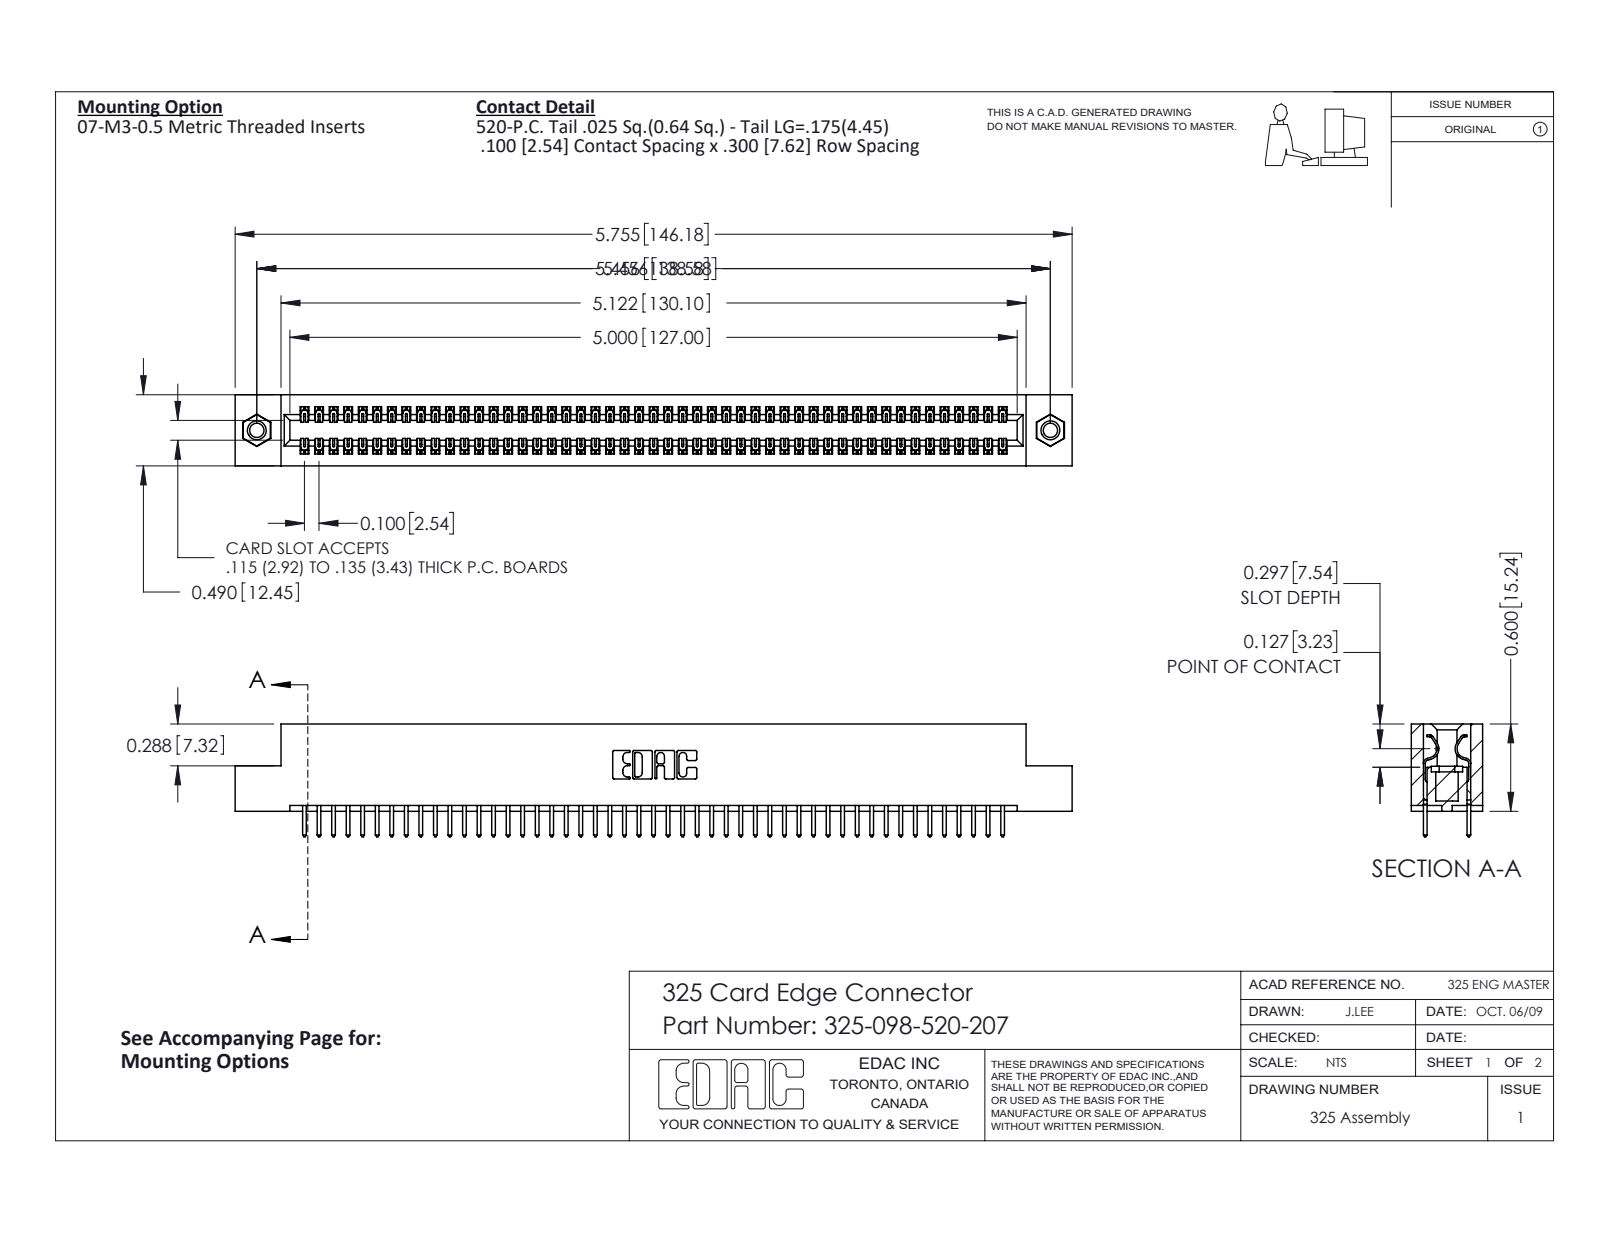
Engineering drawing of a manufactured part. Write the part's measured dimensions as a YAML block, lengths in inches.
part_name: "325 Part_TI; 345-250-001_345-250-005-103; 325-292-001_325-293-120; 325-098-520-207"
step_written_by: "SolidWorks 2016 (CONFIG_CONTROL_DESIGN)"
units: inches
bodies: {solids: 101, faces: 5270, planar: 3630, cylindrical: 1624, other: 16}
overall_size: [5.755, 0.775, 0.49]
volume: 1.154
surface_area: 35.46
round_holes:
  - {diameter: 0.098, count: 2}
  - {diameter: 0.125, count: 2}
  - {diameter: 0.16, count: 2}
round_bosses_or_shafts:
  - {diameter: 0.155, count: 2}
partial_cylinders:
  - {radius: 0.006, count: 147}
  - {radius: 0.01, count: 98}
  - {radius: 0.01, count: 22}
  - {radius: 0.007, count: 6}
  - {radius: 0.031, count: 6}
  - {radius: 0.026, count: 3}
  - {radius: 0.014, count: 2}
  - {radius: 0.022, count: 2}
face_to_face_distances: [0.083, 0.407, 0.3, 0.49, 0.107, 0.383, 0.025, 0.325, 0.275, 0.56]
hole_center_spacings: [5.456]
